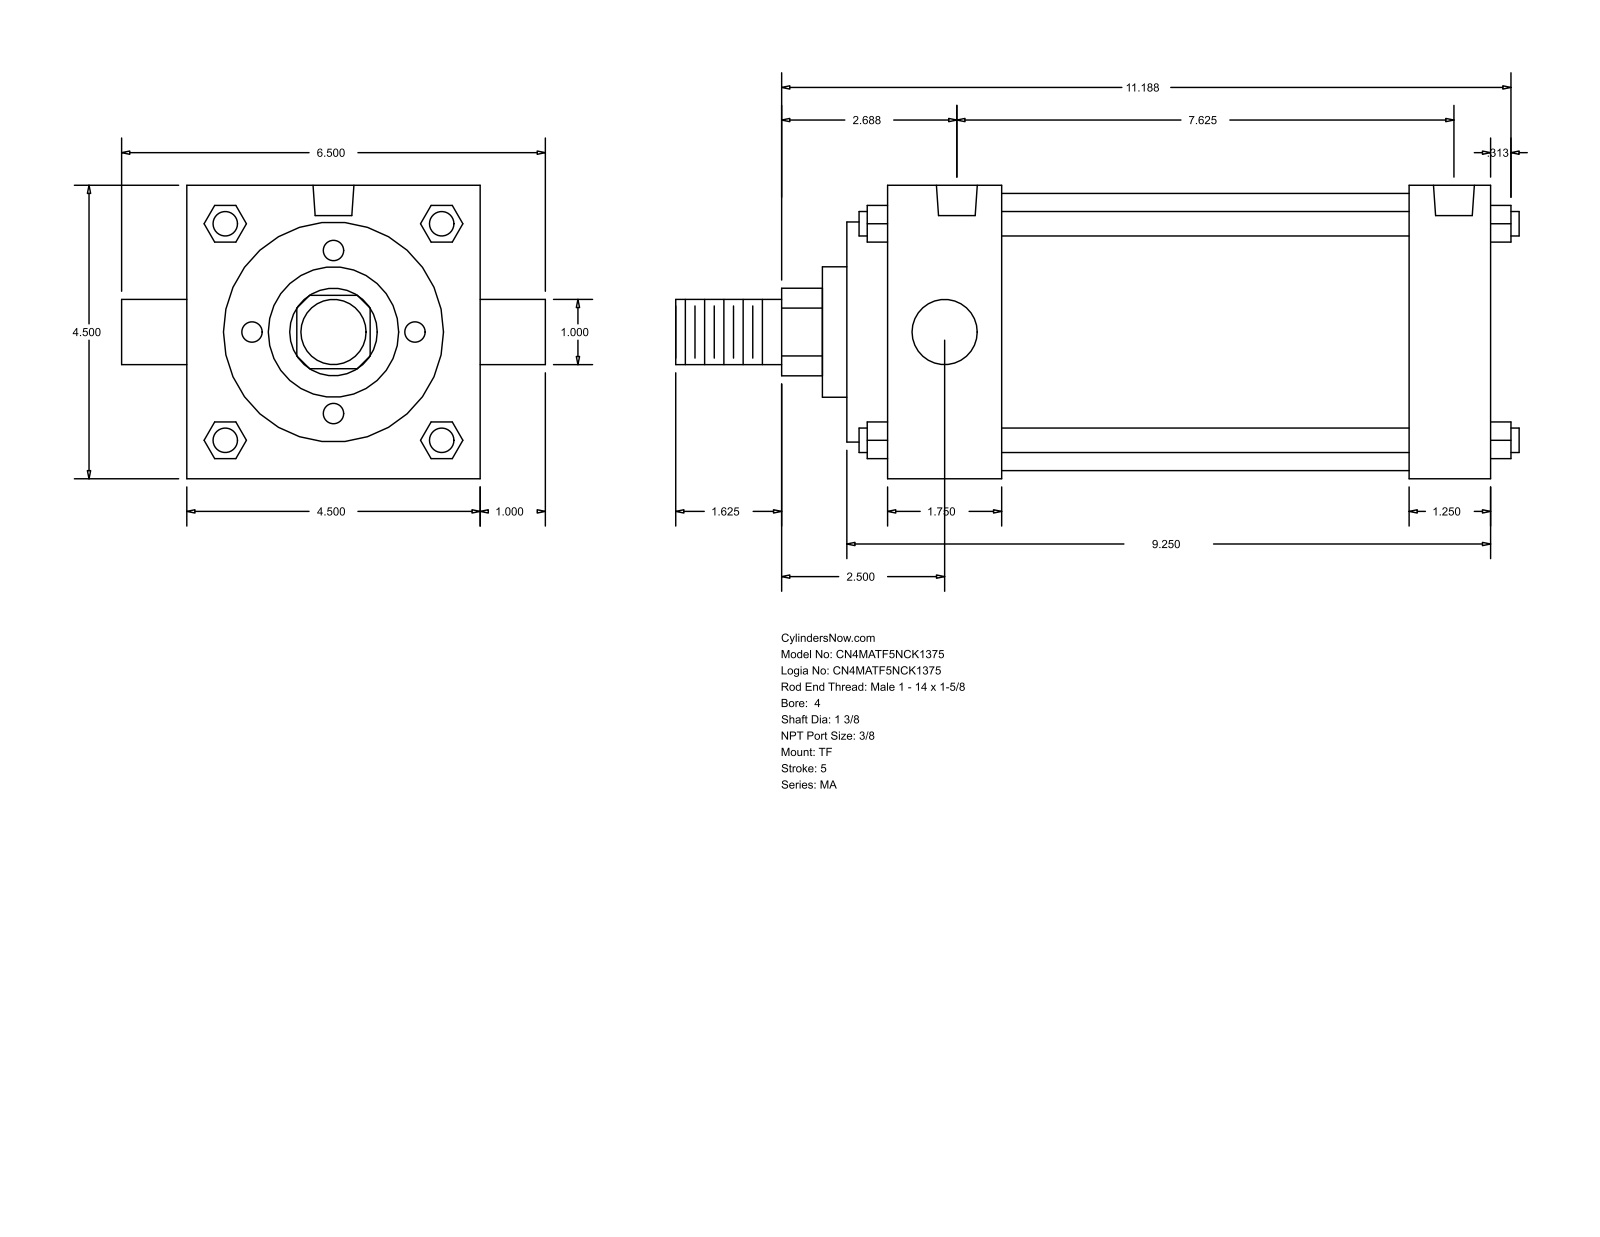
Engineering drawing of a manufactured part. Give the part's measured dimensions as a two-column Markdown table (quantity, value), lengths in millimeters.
| quantity | value |
| --- | --- |
| part name | MA_TF__0400_1.375 |
| STEP written by | GSSL Pune (CONFIG_CONTROL_DESIGN) |
| units | millimeters |
| bodies | 0 solids, 122 faces (93 planar, 29 cylindrical, 0 other) |
| overall size | 328.61 × 165.1 × 114.3 |
| round holes (diameter × count) | 11.11 × 3, 15.93 × 2 |
| round bosses / shafts (diameter × count) | 9.53 × 4, 25.4 × 2, 107.95 × 1, 85.72 × 1, 50.8 × 1, 34.92 × 1 |
| partial cylindrical surfaces (radius × count) | 17.06 × 1 |
| main face-to-face distances | 114.3, 234.96, 15.87, 250.83, 219.07, 203.2, 31.76, 60.32, 44.45, 158.75 |
| hole center spacings | 4.76, 4.77, 184.15, 188.91, 188.92, 193.68 |
